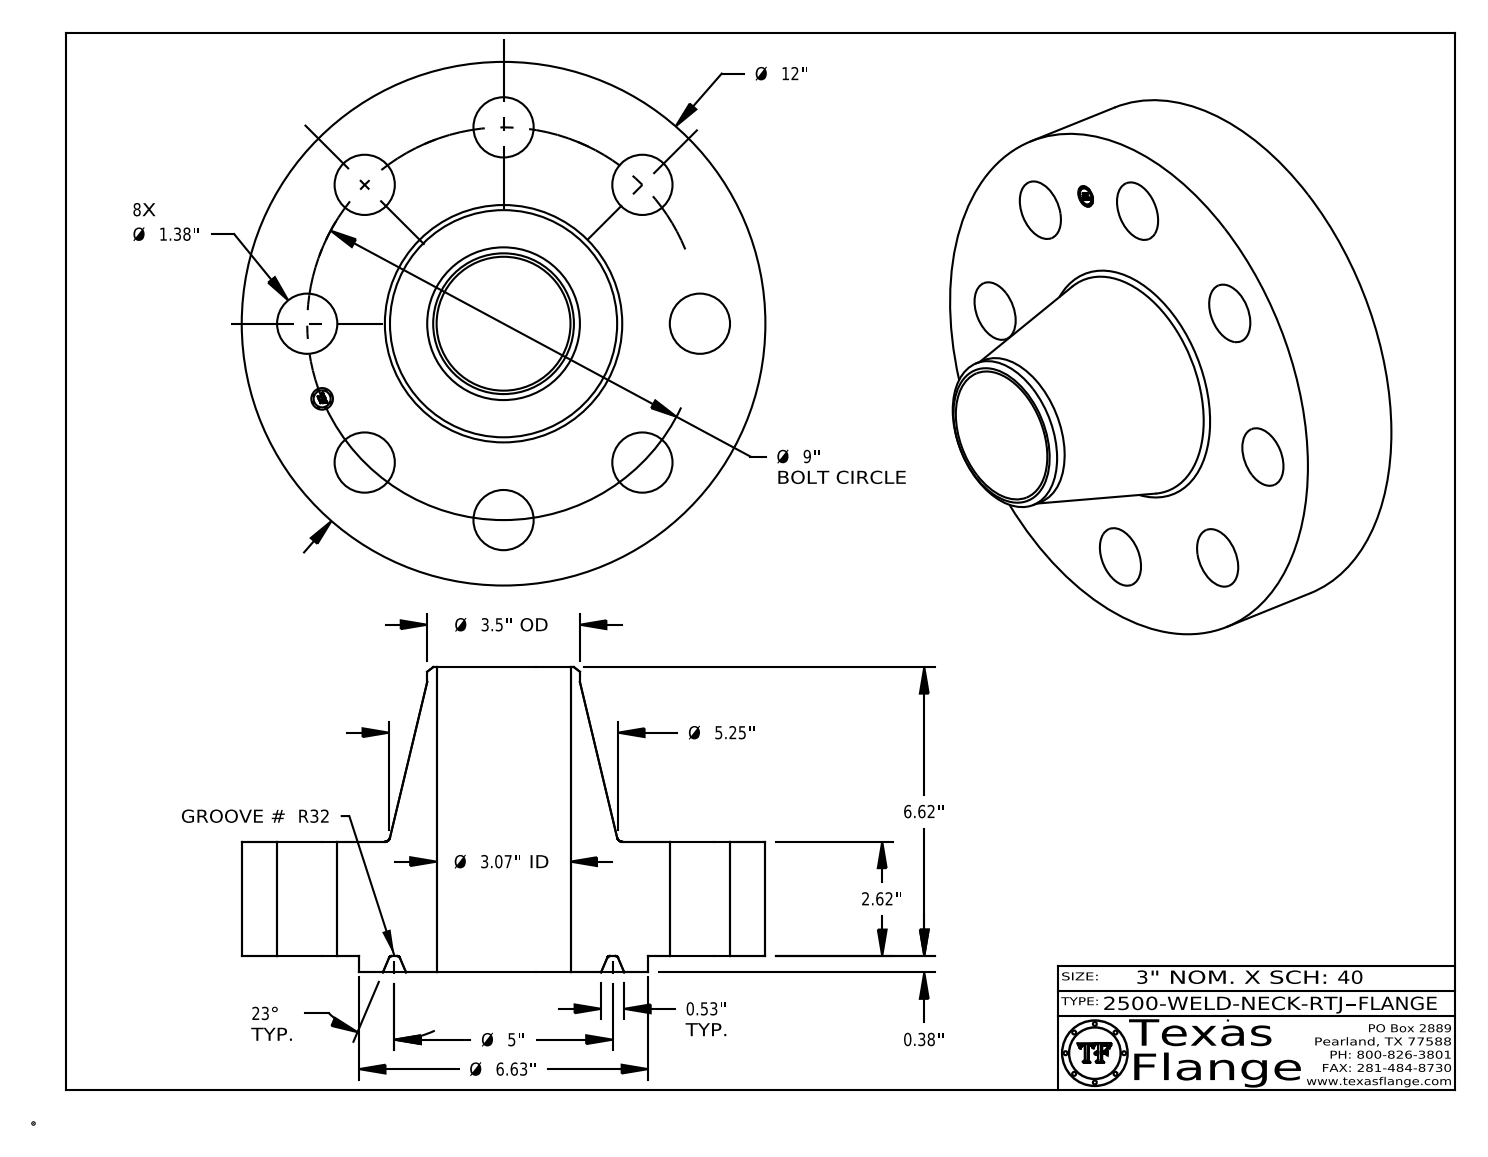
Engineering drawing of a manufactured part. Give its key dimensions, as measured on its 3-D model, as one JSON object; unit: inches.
{"part_name": "2500-WELD-NECK-RTJ", "step_written_by": "CATIA V5 STEP AP214 (AUTOMOTIVE_DESIGN)", "units": "inches", "bodies": {"solids": 1, "faces": 429, "planar": 371, "cylindrical": 44, "other": 14}, "overall_size": [12, 12, 6.995], "volume_in3": 283, "surface_area_in2": 502.1, "round_holes": [[1.38, 8], [0.495, 1], [3.068, 1]], "round_bosses_or_shafts": [[0.03, 8], [12, 1], [6.625, 1], [3.5, 1], [0.39, 1]], "face_to_face_distances": [2.62, 0.375, 2.995, 6.995, 6.62, 4, 2.98, 2.605, 0.015, 4.015], "hole_center_spacings": [4.5, 3.444, 6.364, 8.315, 1.756, 5, 7.483, 9]}
